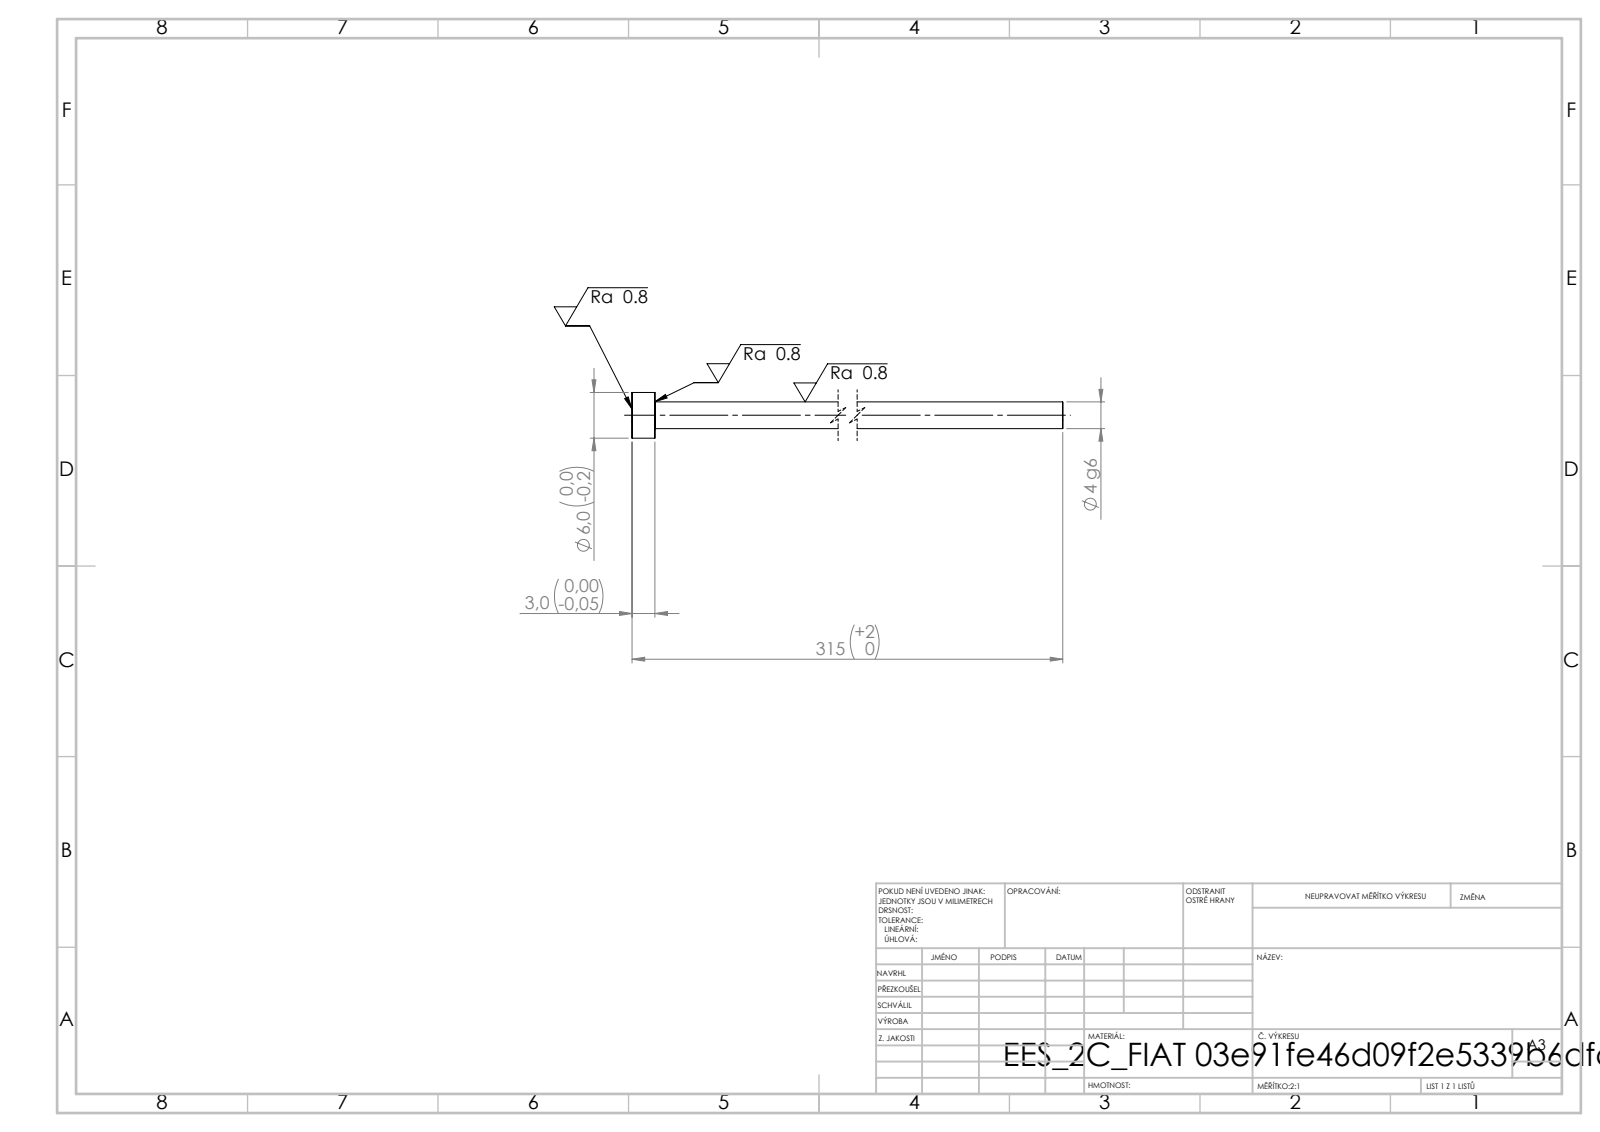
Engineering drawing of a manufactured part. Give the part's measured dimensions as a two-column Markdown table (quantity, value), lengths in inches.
| quantity | value |
| --- | --- |
| STEP written by | SolidWorks 2019 (CONFIG_CONTROL_DESIGN) |
| units | inches |
| bodies | 1 solid, 7 faces (3 planar, 4 cylindrical, 0 other) |
| overall size | 12.402 × 0.236 × 0.236 |
| volume | 0.188 in³ |
| surface area | 5.493 in² |
| round bosses / shafts (diameter × count) | 0.236 × 1, 0.138 × 1 |
| main face-to-face distances | 0.118, 12.402, 12.283 |
